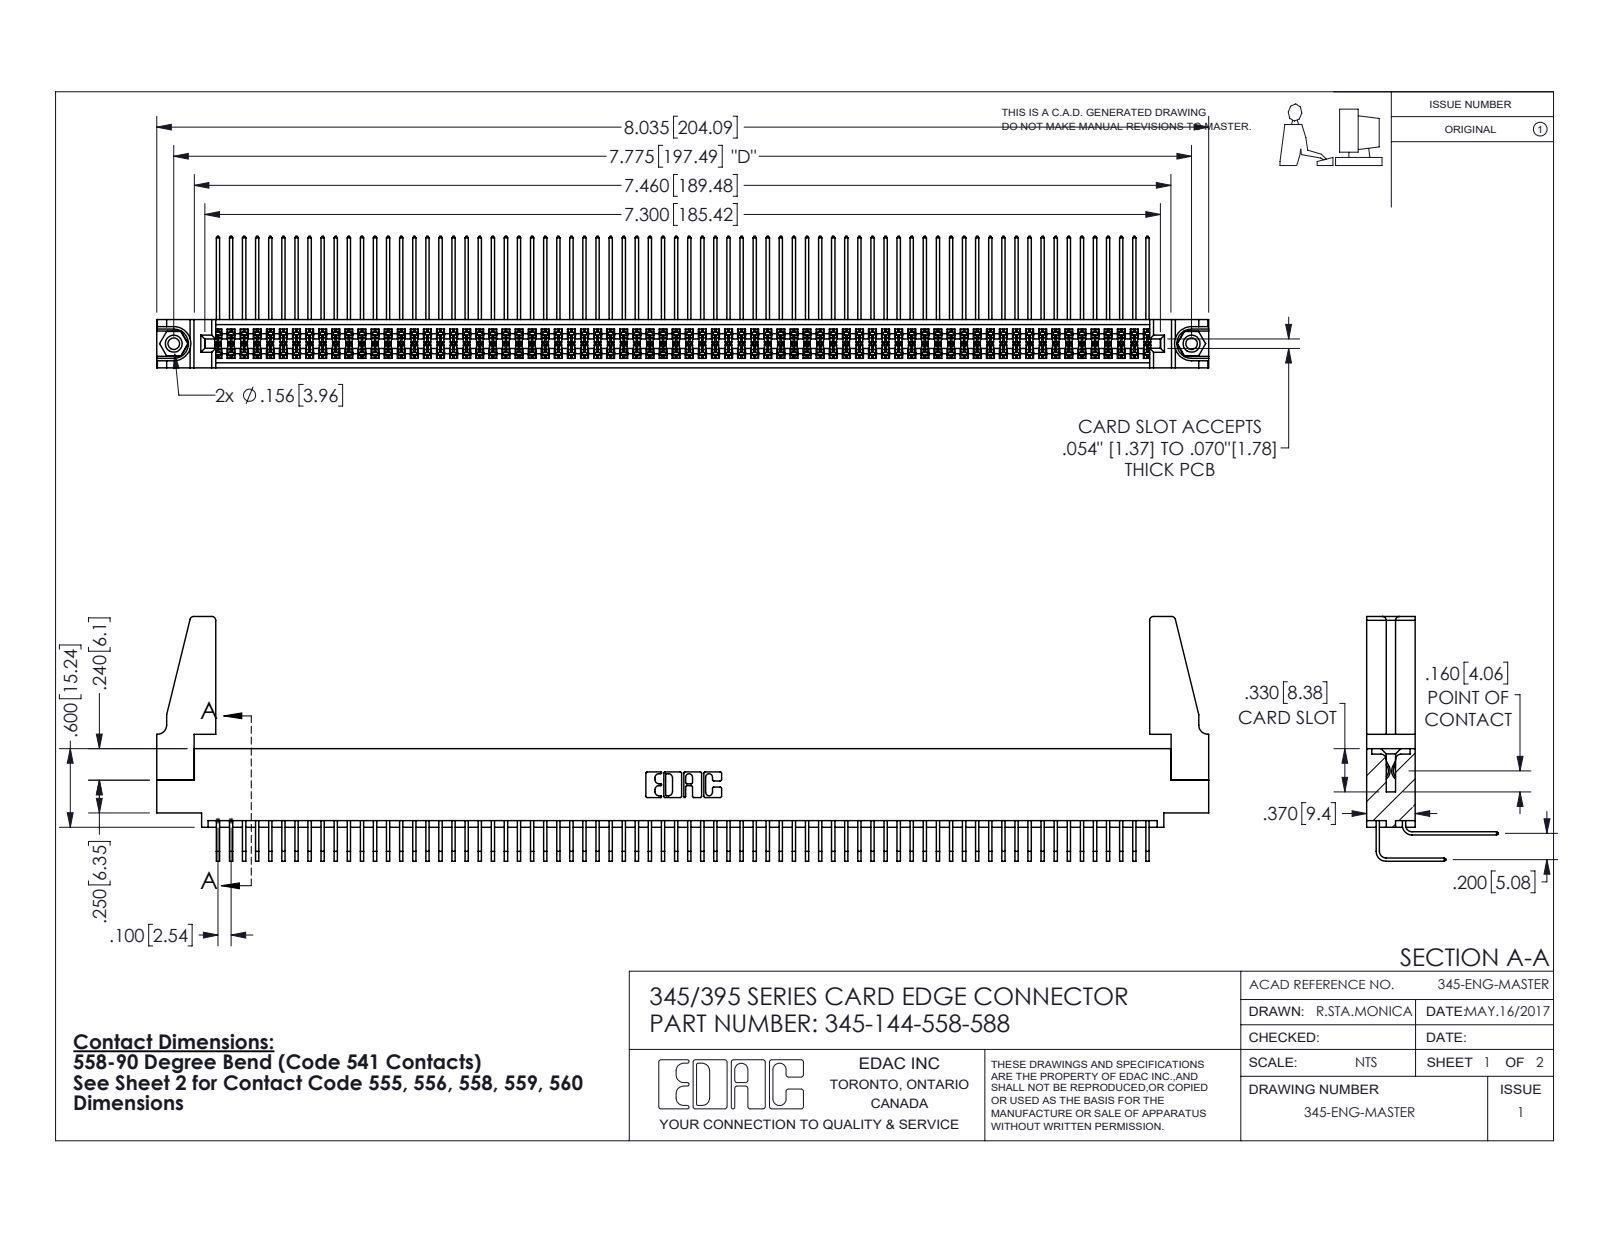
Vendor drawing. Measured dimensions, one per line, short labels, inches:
name: 345-144-558-588; 345-292-001_558 559 Tail - 1; 345-220-078_345-220-088; 345 Part_0.110 Offset - 0.156 Dia-TH (+2 more)
written by: SolidWorks 2016 (CONFIG_CONTROL_DESIGN)
unit: in
bodies: 149 solids, 7742 faces (5196 planar, 2530 cylindrical, 16 other)
size: 8.036 × 1.869 × 1.005
volume: 1.472 in³; area: 59.74 in²
holes: 2× ⌀0.089, 2× ⌀0.125, 2× ⌀0.156, 1× ⌀0.064
bosses: 2× ⌀0.155
rounds: 287× R0.006, 22× R0.01, 8× R0.03, 6× R0.007, 6× R0.031, 3× R0.026, 2× R0.014, 2× R0.019
face distances: 0.072, 0.298, 0.2, 0.37, 0.098, 0.272, 0.025, 0.225, 0.025, 0.175
hole spacings: 0.27, 7.539, 7.775
